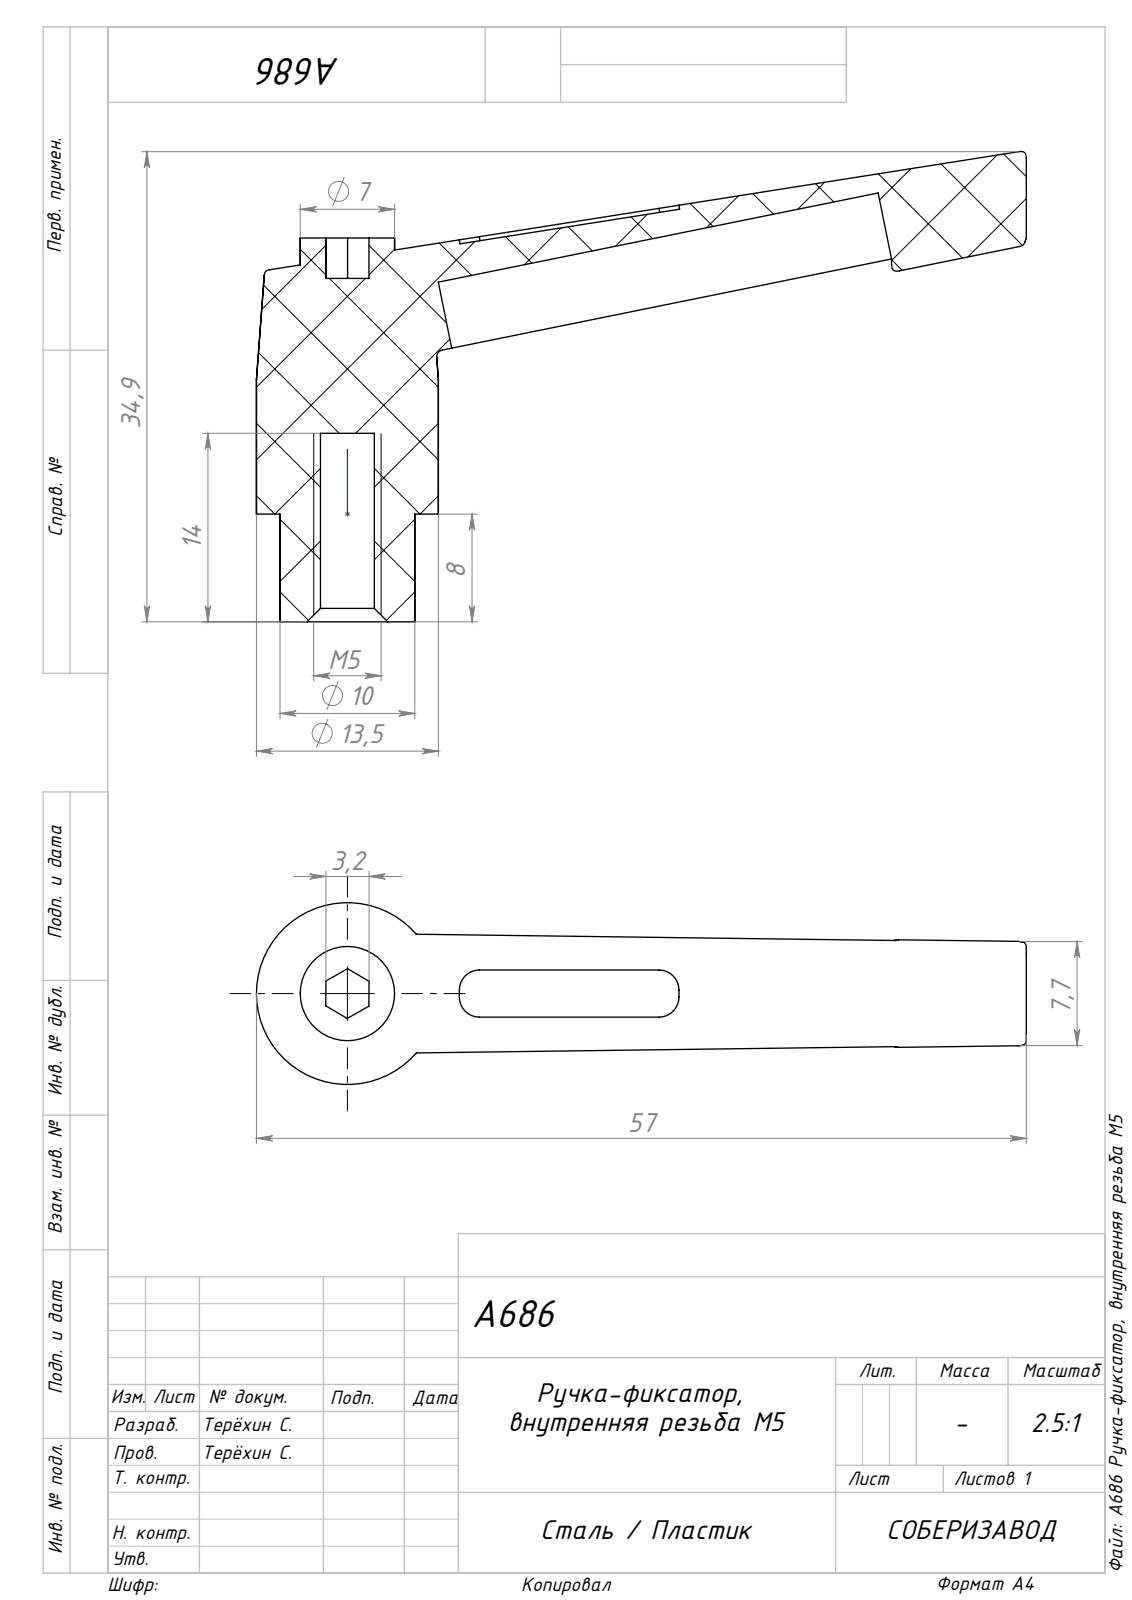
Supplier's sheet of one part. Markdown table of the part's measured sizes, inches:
| quantity | value |
| --- | --- |
| part name | A686 Ручка-фиксатор, внутренняя резьба М5; A686 Ручка-фиксатор, внутренняя резьба М5_Резьба схематическая |
| STEP written by | SolidWorks 2026 (CONFIG_CONTROL_DESIGN) |
| units | inches |
| bodies | 1 solid, 79 faces (29 planar, 12 cylindrical, 38 other) |
| overall size | 2.249 × 1.375 × 0.531 |
| volume | 0.268 in³ |
| surface area | 5.078 in² |
| round holes (diameter × count) | 0.157 × 1 |
| round bosses / shafts (diameter × count) | 0.531 × 1, 0.394 × 1, 0.276 × 1 |
| partial cylindrical surfaces (radius × count) | 0.059 × 4 |
| main face-to-face distances | 0.236, 0.315, 1.311, 1.122, 0.807, 0.126, 0.551, 0.236, 0.571, 1.004 |
